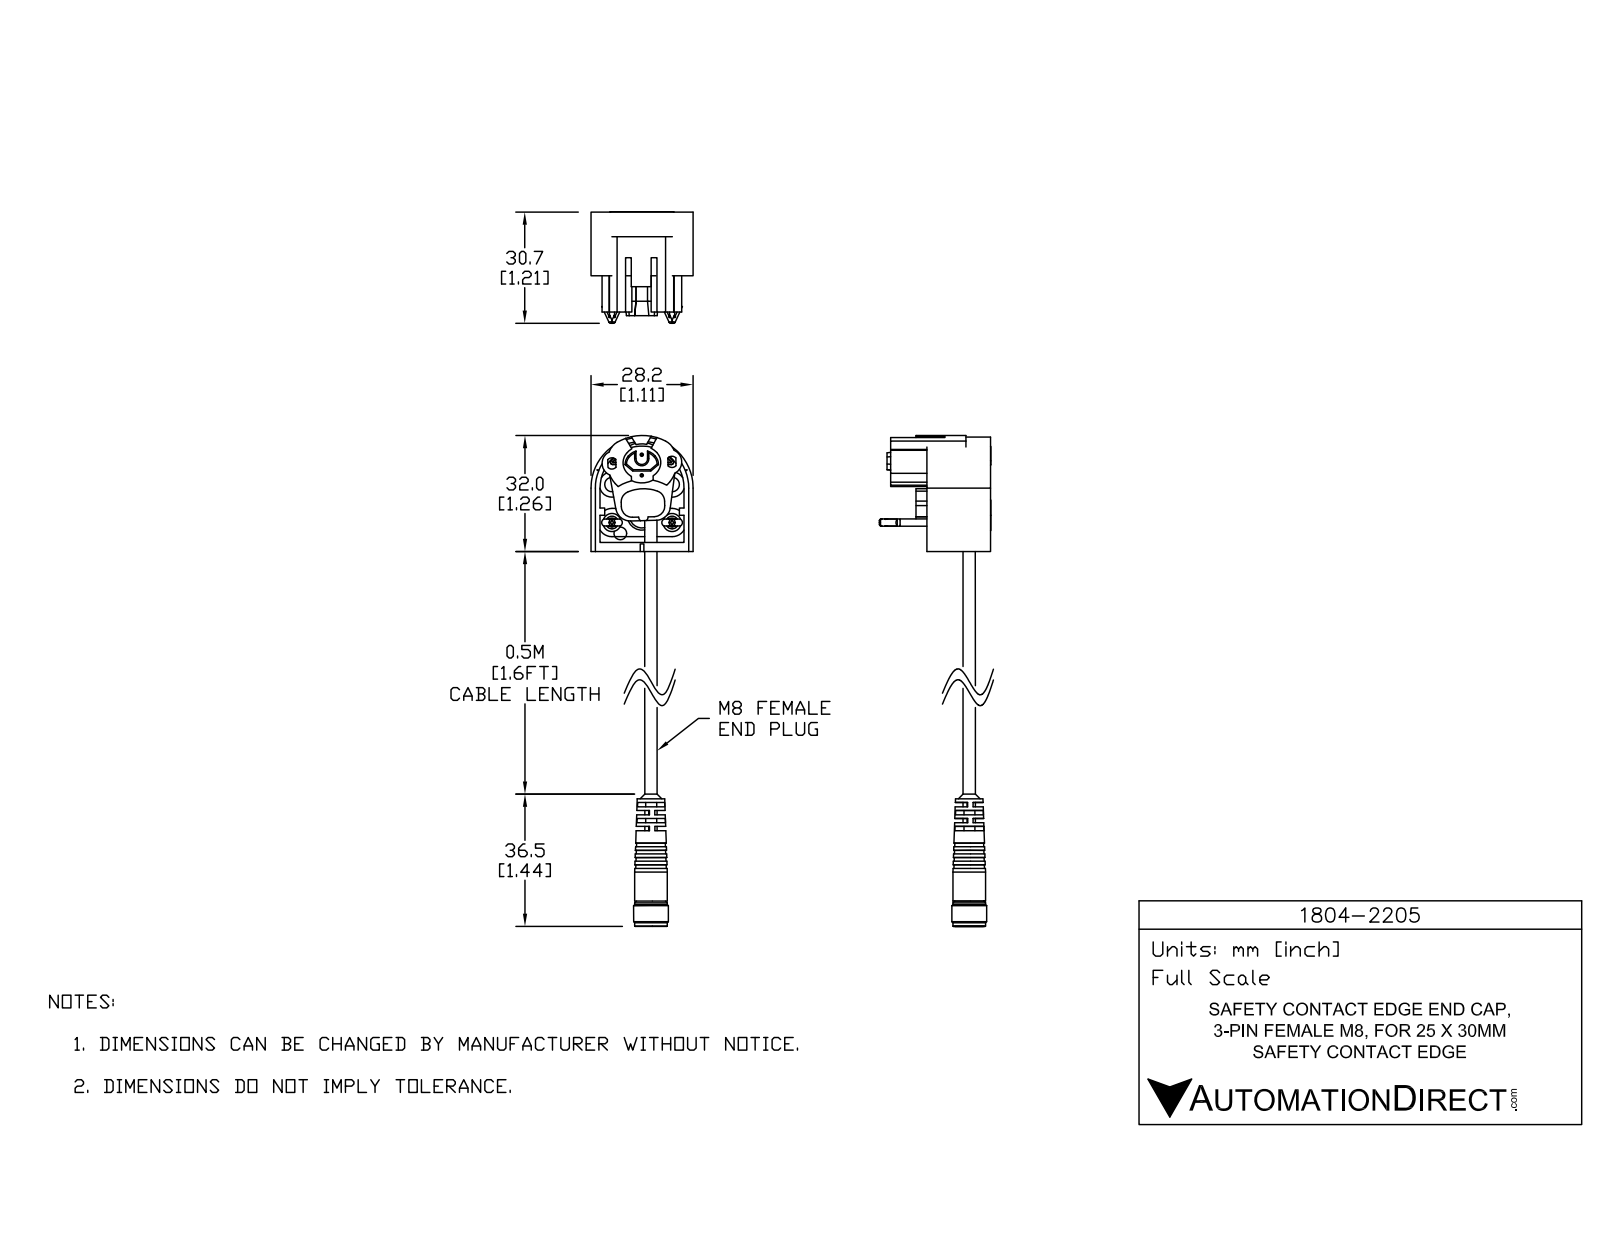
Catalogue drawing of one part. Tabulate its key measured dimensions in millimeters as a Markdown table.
| quantity | value |
| --- | --- |
| part name | 1804-2205 |
| STEP written by | SolidWorks 2018 (AUTOMOTIVE_DESIGN) |
| units | millimeters |
| bodies | 4 solids, 397 faces (199 planar, 135 cylindrical, 63 other) |
| overall size | 140.6 × 30.8 × 28.2 |
| volume | 12 100 mm³ |
| surface area | 13 060 mm² |
| round holes (diameter × count) | 1.5 × 5, 0.5 × 4, 3.5 × 3, 0.9 × 2, 3.1 × 2, 4 × 2, 5.5 × 2, 6.9 × 2, 5.9 × 1, 7.2 × 1 |
| round bosses / shafts (diameter × count) | 9 × 2, 5.7 × 2, 5 × 2, 3.5 × 2, 2.5 × 2, 2 × 2, 0.7 × 2, 9.6 × 1 |
| partial cylindrical surfaces (radius × count) | 1 × 8, 3 × 6, 3.5 × 6, 4 × 4, 5 × 4, 3.9 × 2, 4.1 × 2, 5.1 × 2 |
| main face-to-face distances | 1.8, 2.5, 1, 0.8, 10.8, 28.2, 5.8, 1.3, 11.6, 5 |
| hole center spacings | 1.8, 16.6, 1.4, 1.8, 2.5, 8.8, 24.1, 24.8 |
